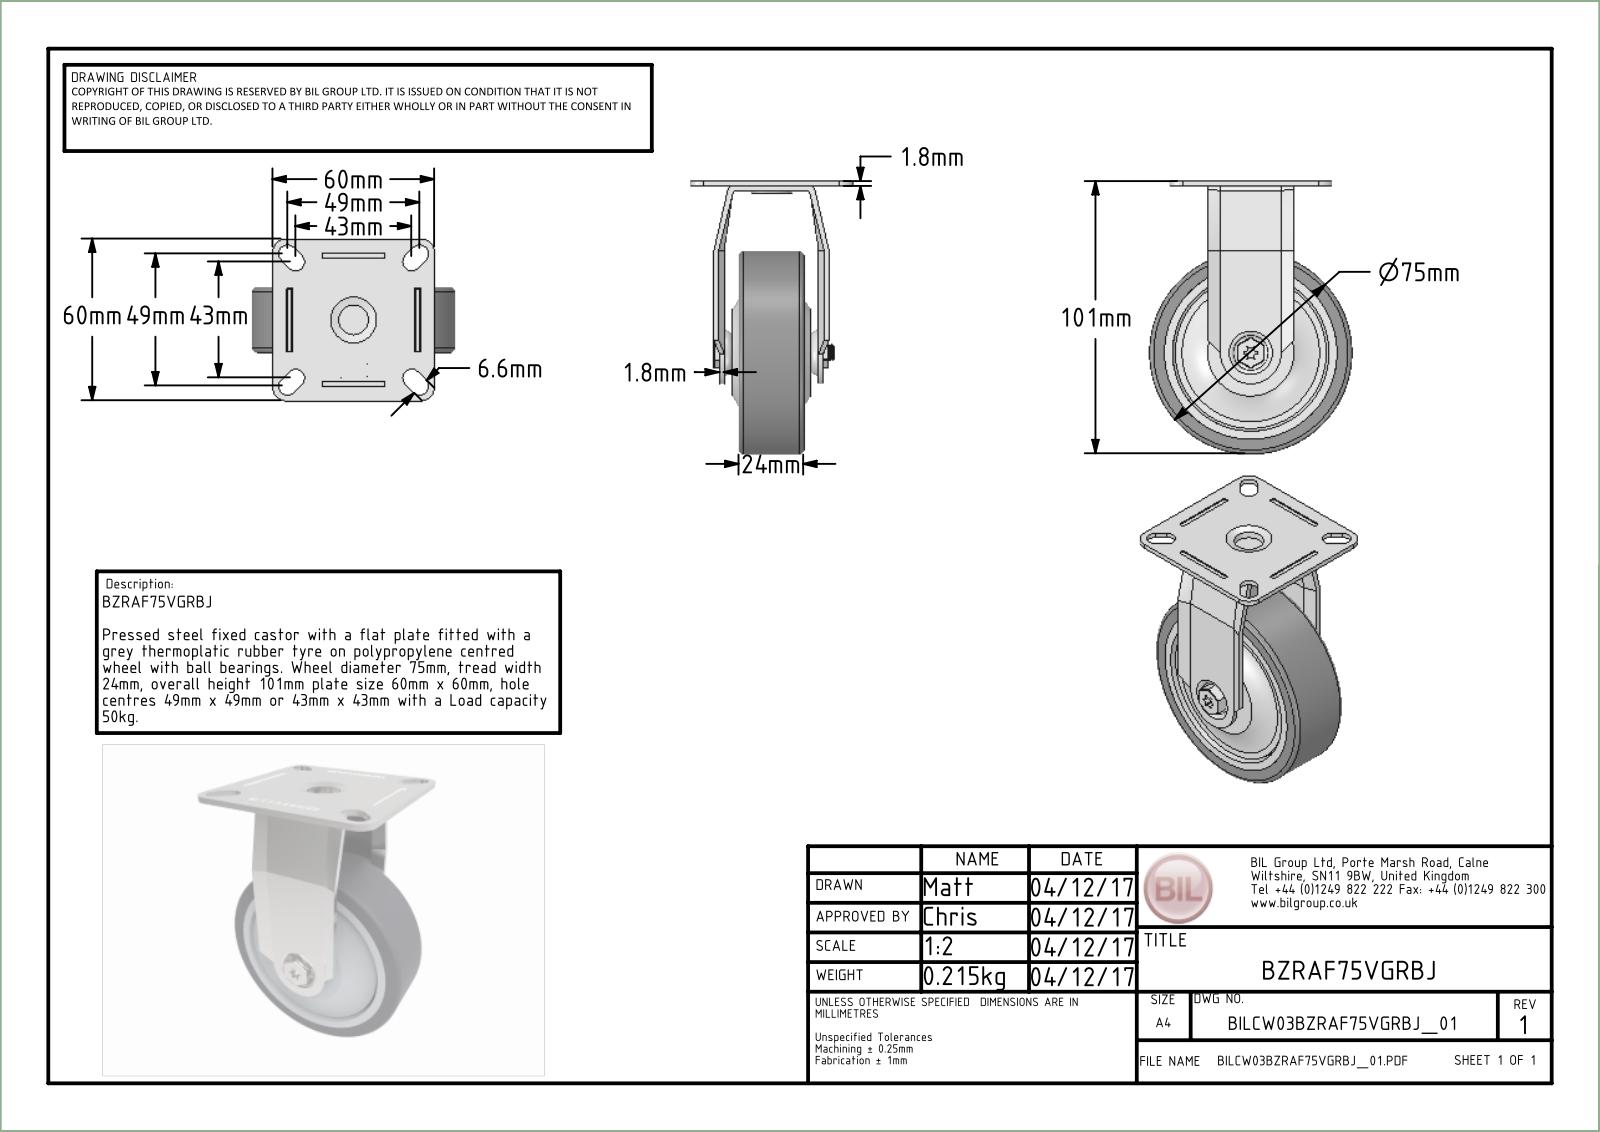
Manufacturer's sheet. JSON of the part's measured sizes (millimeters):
{"part_name": "BZRAF75VGRBJ v2; BZRAF75AS v1; ZINC PLATED PRESSED STEEL TOP PLATE; ZINC PLATED PRESSED STEEL FORKS (+7 more)", "step_written_by": "Autodesk Translation Framework v13.20.0.188 (AP242_MANAGED_MODEL_BASED_3D_ENGINEERING_MIM_LF)", "units": "millimeters", "bodies": {"solids": 19, "faces": 482, "planar": 152, "cylindrical": 163, "other": 167}, "overall_size": [101, 75, 60], "volume_mm3": 86890, "surface_area_mm2": 67141, "round_holes": [[6, 1], [6.2, 1], [8.2, 1], [10.55, 1], [11.2, 1], [11.5, 1], [12, 1], [12.74, 1], [16, 1], [18.3, 1], [19.2, 1], [19.88, 1]], "round_bosses_or_shafts": [[56, 1], [30.75, 1], [18.7, 1], [18.32, 1], [15, 1], [14, 1], [11.6, 1], [10, 1]], "partial_cylinders_radius": [[1, 34], [0.5, 20], [1.5, 8], [3.3, 8], [0.4, 6], [0.99, 4], [4.5, 4], [1.8, 2]], "face_to_face_distances": [1.8, 10.25, 13.75, 6.25, 2, 3.25, 2.25, 9.75, 7.5, 24.25]}
